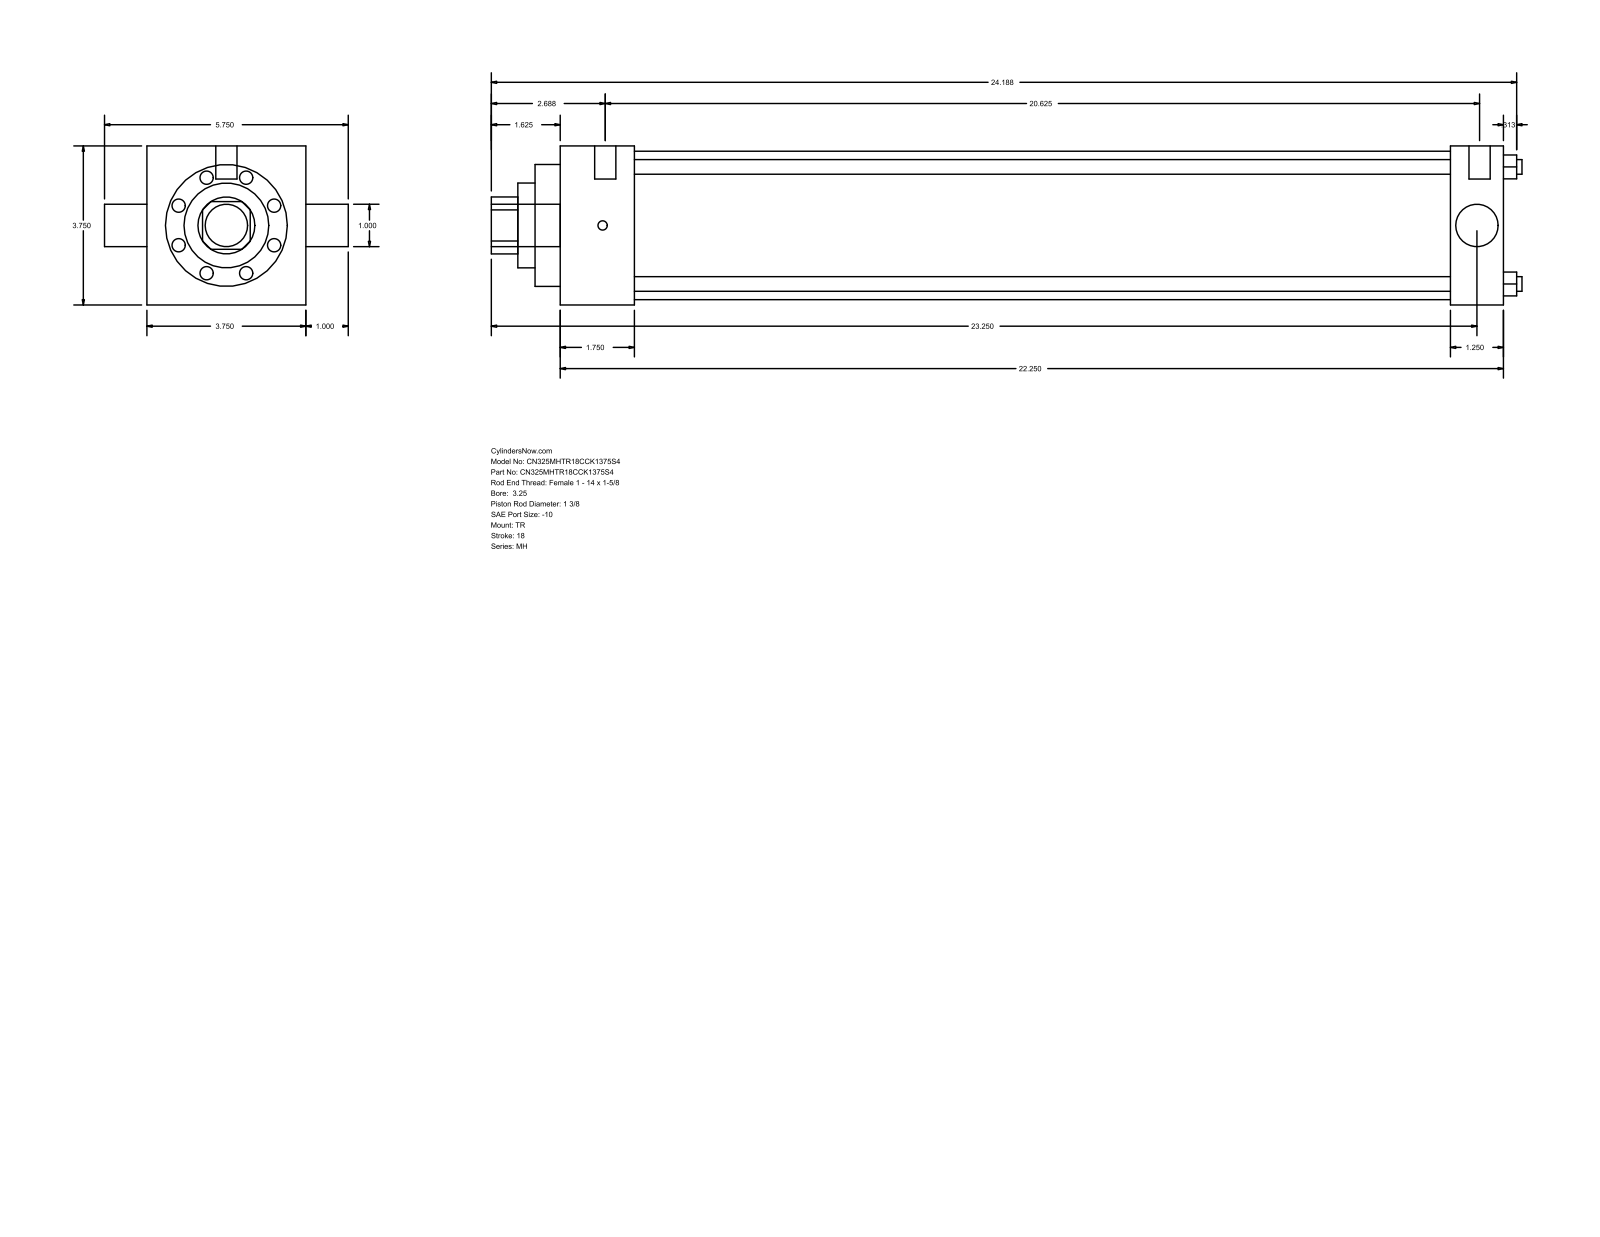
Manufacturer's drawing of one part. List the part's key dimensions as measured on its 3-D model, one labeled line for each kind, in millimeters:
Part name (STEP PRODUCT): MH_TR__0325_1.375
STEP written by: GSSL Pune (CONFIG_CONTROL_DESIGN)
Units: millimetres
Bodies: 0 solids, 86 faces (61 planar, 25 cylindrical, 0 other)
Overall size (bounding box): 617.54 × 146.05 × 95.25
Round holes (diameter × count): ⌀8.76 ×4, ⌀25.4 ×1, ⌀34.92 ×1, ⌀50.8 ×1, ⌀73.03 ×1, ⌀88.9 ×1
Round bosses / shafts (diameter × count): ⌀5.56 ×3, ⌀12.7 ×2, ⌀25.4 ×1
Partial cylindrical surfaces — rounded edges, fillets, slot ends (radius × count): R17.06 ×1
Main face-to-face distances: 95.24, 565.15, 44.45, 533.4, 488.95, 520.7, 31.75, 15.08, 59.53, 548.48
Hole centre spacings: 49.57, 70.1, 99.14
